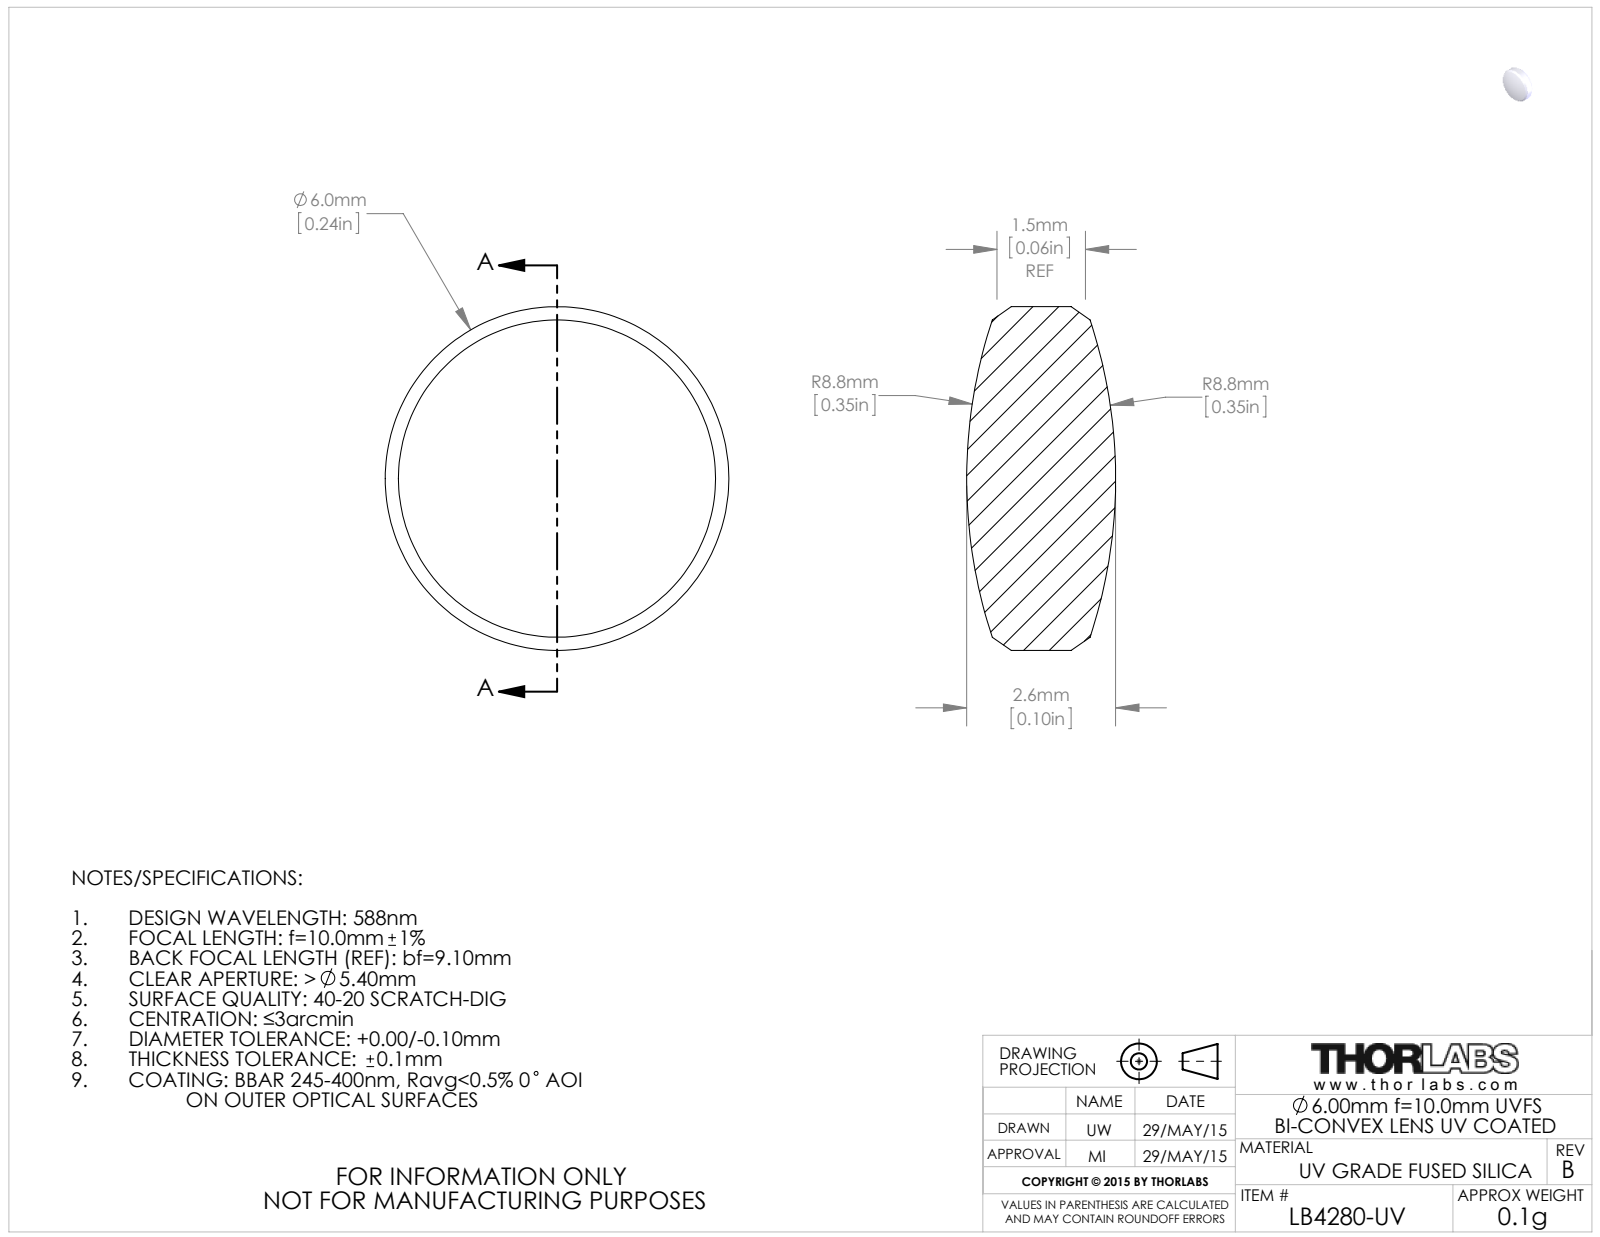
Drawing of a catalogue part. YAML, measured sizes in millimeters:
part_name: "4307-E0W"
step_written_by: "SolidWorks 2014 (CONFIG_CONTROL_DESIGN)"
units: millimeters
bodies: {solids: 1, faces: 10, planar: 0, cylindrical: 2, other: 8}
overall_size: [6, 6, 2.6]
volume: 58
surface_area: 84
round_bosses_or_shafts:
  - {diameter: 6, count: 1}
